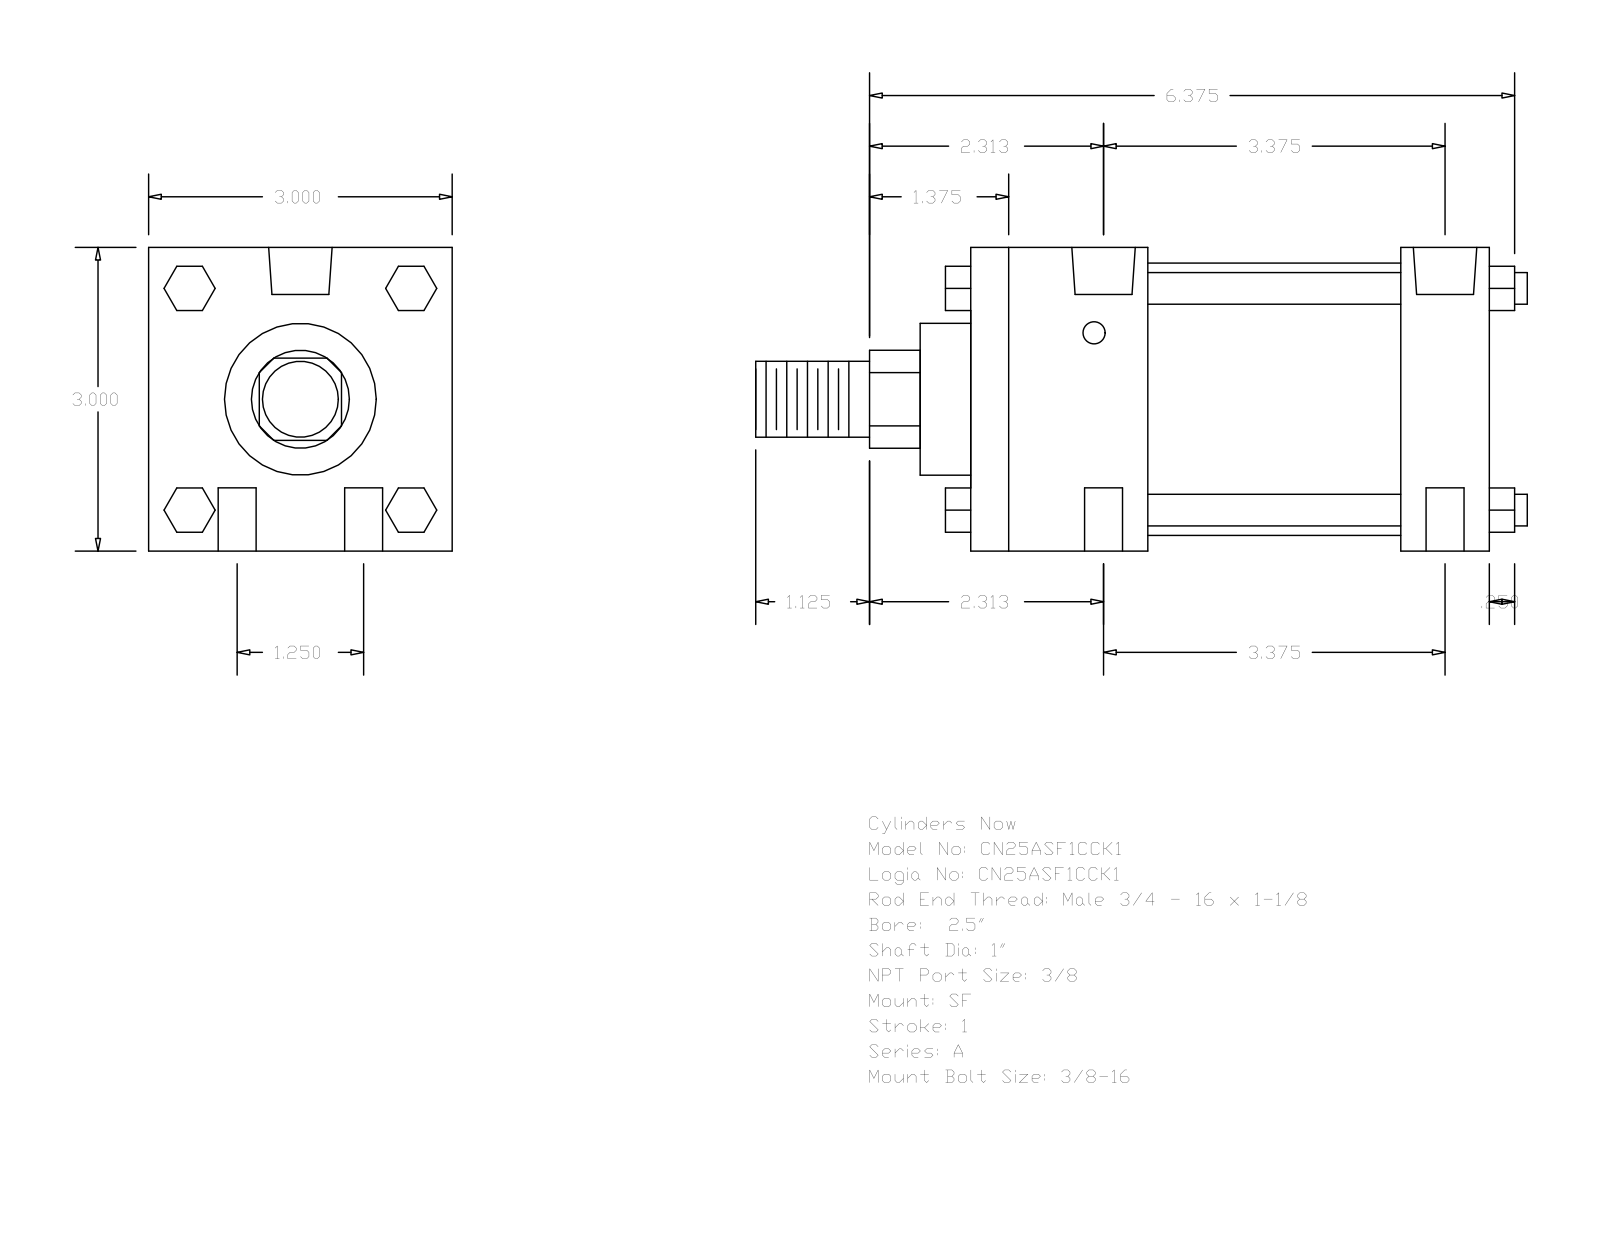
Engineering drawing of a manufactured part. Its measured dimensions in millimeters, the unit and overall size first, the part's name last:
Units: millimetres
Overall size (bounding box): 193.68 × 76.2 × 76.2
Round holes (diameter × count): ⌀9.53 ×4, ⌀5.56 ×2, ⌀15.93 ×2
Round bosses / shafts (diameter × count): ⌀7.94 ×4, ⌀68.33 ×1, ⌀38.1 ×1, ⌀25.4 ×1, ⌀19.05 ×1
Partial cylindrical surfaces — rounded edges, fillets, slot ends (radius × count): R12.29 ×1
Main face-to-face distances: 76.2, 130.17, 63.5, 107.95, 22.22, 44.45, 85.72, 12.7, 11.11, 57.15
Hole centre spacings: 15.88, 87.18, 85.72, 31.76, 91.41, 90.48
Bodies: 0 solids, 124 faces (94 planar, 30 cylindrical, 0 other)
Part name (STEP PRODUCT): A_SF__0250_1
STEP written by: GSSL Pune (CONFIG_CONTROL_DESIGN)
